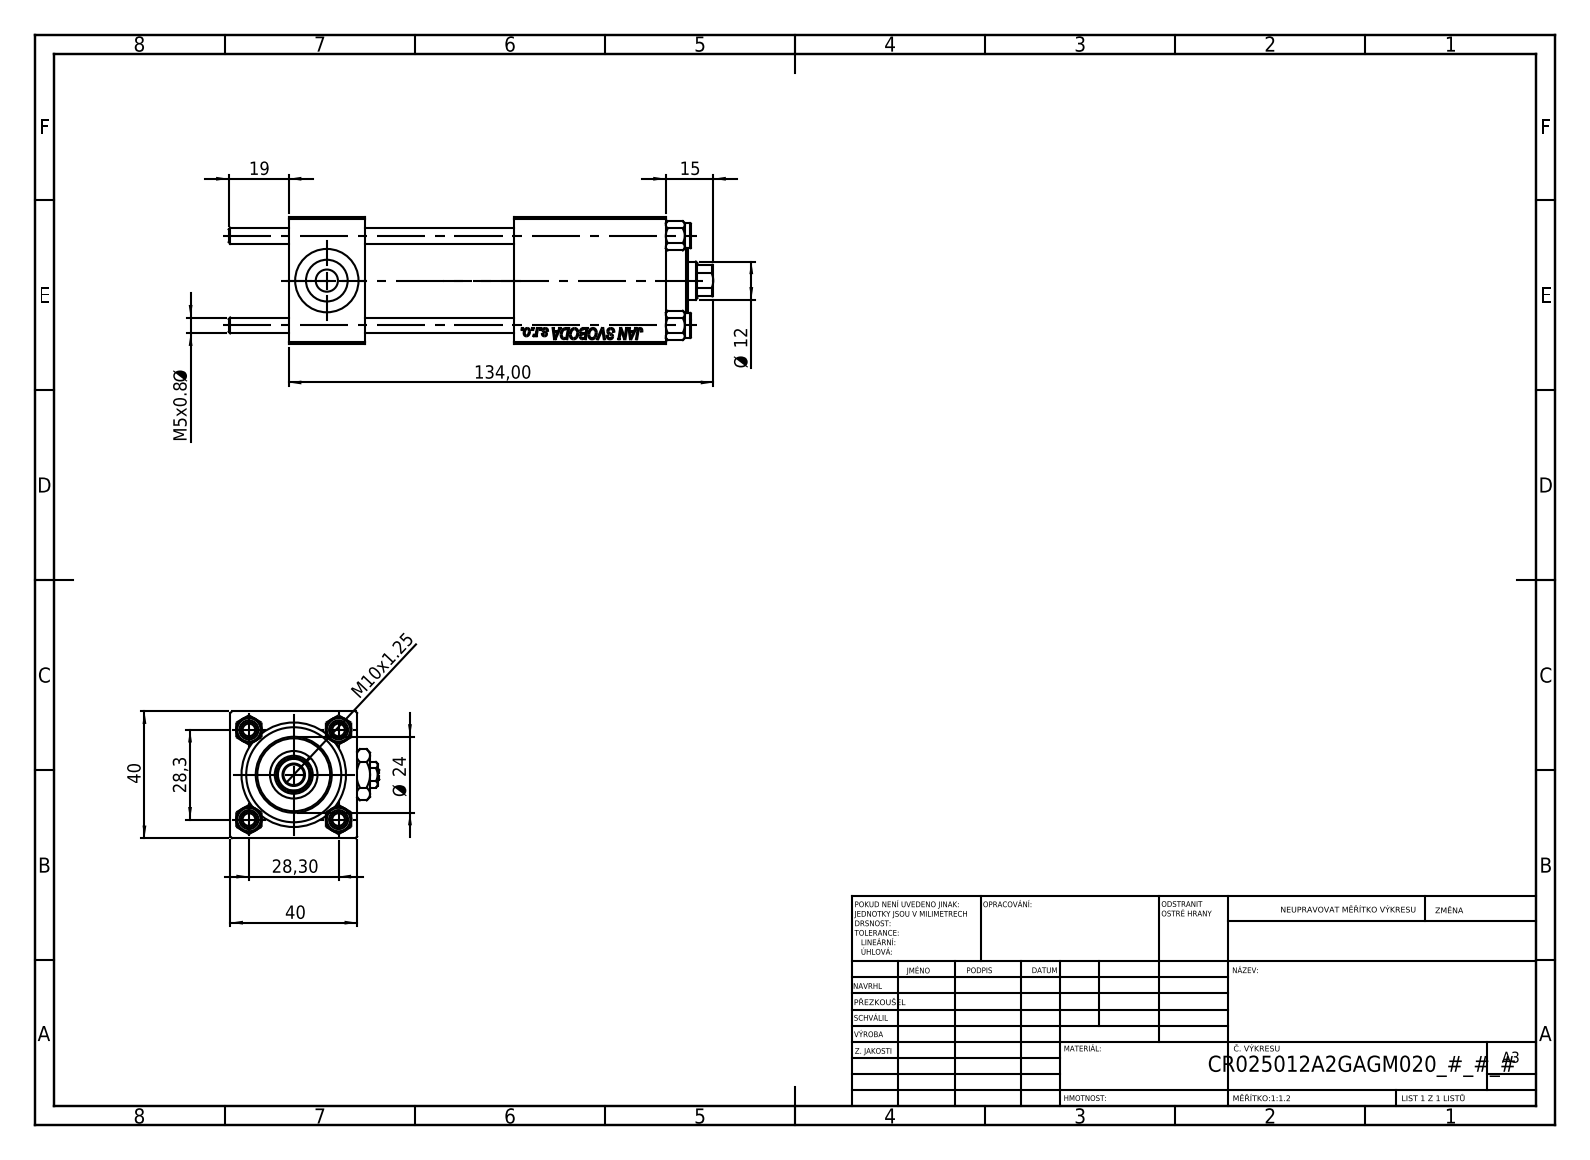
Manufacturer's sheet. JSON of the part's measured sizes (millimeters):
{"part_name": "V215CR_VCP; Zatka_pro_OIL_PORT; V215CR_BODY_A; NUT_M5 (+2 more)", "step_written_by": "SolidWorks 2019 (CONFIG_CONTROL_DESIGN)", "units": "millimeters", "bodies": {"solids": 12, "faces": 1184, "planar": 540, "cylindrical": 86, "other": 558}, "overall_size": [153, 47, 40], "volume_mm3": 143704, "surface_area_mm2": 59957, "round_holes": [[5, 4], [20, 3], [7, 2], [13.16, 2], [6.5, 1], [12, 1], [13, 1], [15, 1], [25, 1], [30, 1]], "round_bosses_or_shafts": [[8, 4], [31, 1], [24, 1]], "partial_cylinders_radius": [[5.5, 1]], "face_to_face_distances": [40, 24, 119, 95, 90.3, 66.3, 28.7, 19.3, 71, 47], "hole_center_spacings": [20.01, 28.3, 40.02]}
